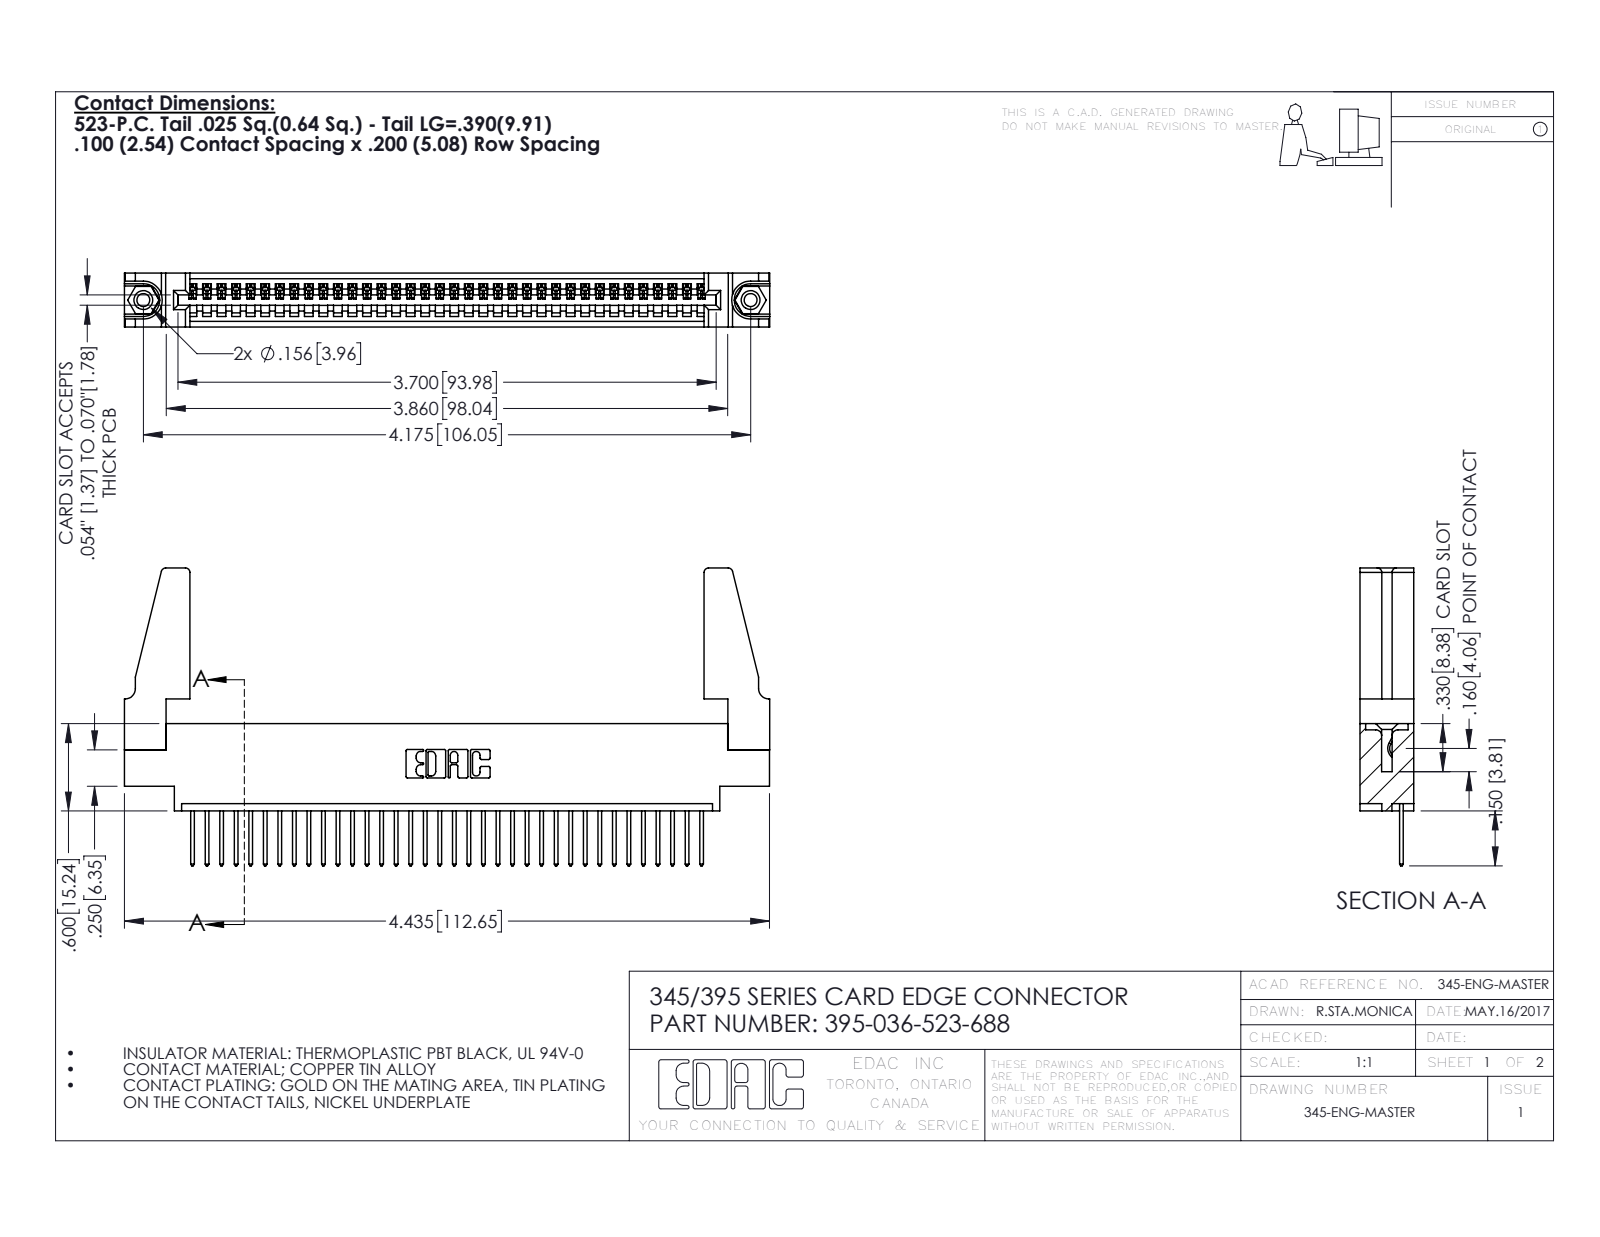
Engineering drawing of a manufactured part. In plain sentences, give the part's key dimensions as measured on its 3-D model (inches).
The part is named "345-220-078_345-220-088; 395-036-523-688; 345-250-001_345-250-001-102; 345 Part_0.170 Offset - 0.156 Dia-TH (+1 more)". Its 3-D file was written by "SolidWorks 2016 (CONFIG_CONTROL_DESIGN)". It is 41 solids with 2342 faces: 1596 planar, 730 cylindrical and 16 other. Overall it measures 4.436 by 2.047 by 0.37 inches. Its volume is 0.841 cubic inches and its surface area 26.66 square inches. Round holes: 2 of diameter 0.089, 2 of diameter 0.125, 2 of diameter 0.156, 1 of diameter 0.064. Round bosses or shafts: 2 of diameter 0.155. Partial cylindrical surfaces (rounded edges, fillets, slot ends): 72 of radius 0.006, 72 of radius 0.01, 22 of radius 0.01, 8 of radius 0.03, 6 of radius 0.007, 6 of radius 0.031, 3 of radius 0.026, 2 of radius 0.031. The main face-to-face distances are 0.072, 0.37, 0.298, 0.098, 0.272, 0.025, 0.2, 0.225, 0.175, 0.149. The hole center spacings are 0.27, 3.939, 4.175.
